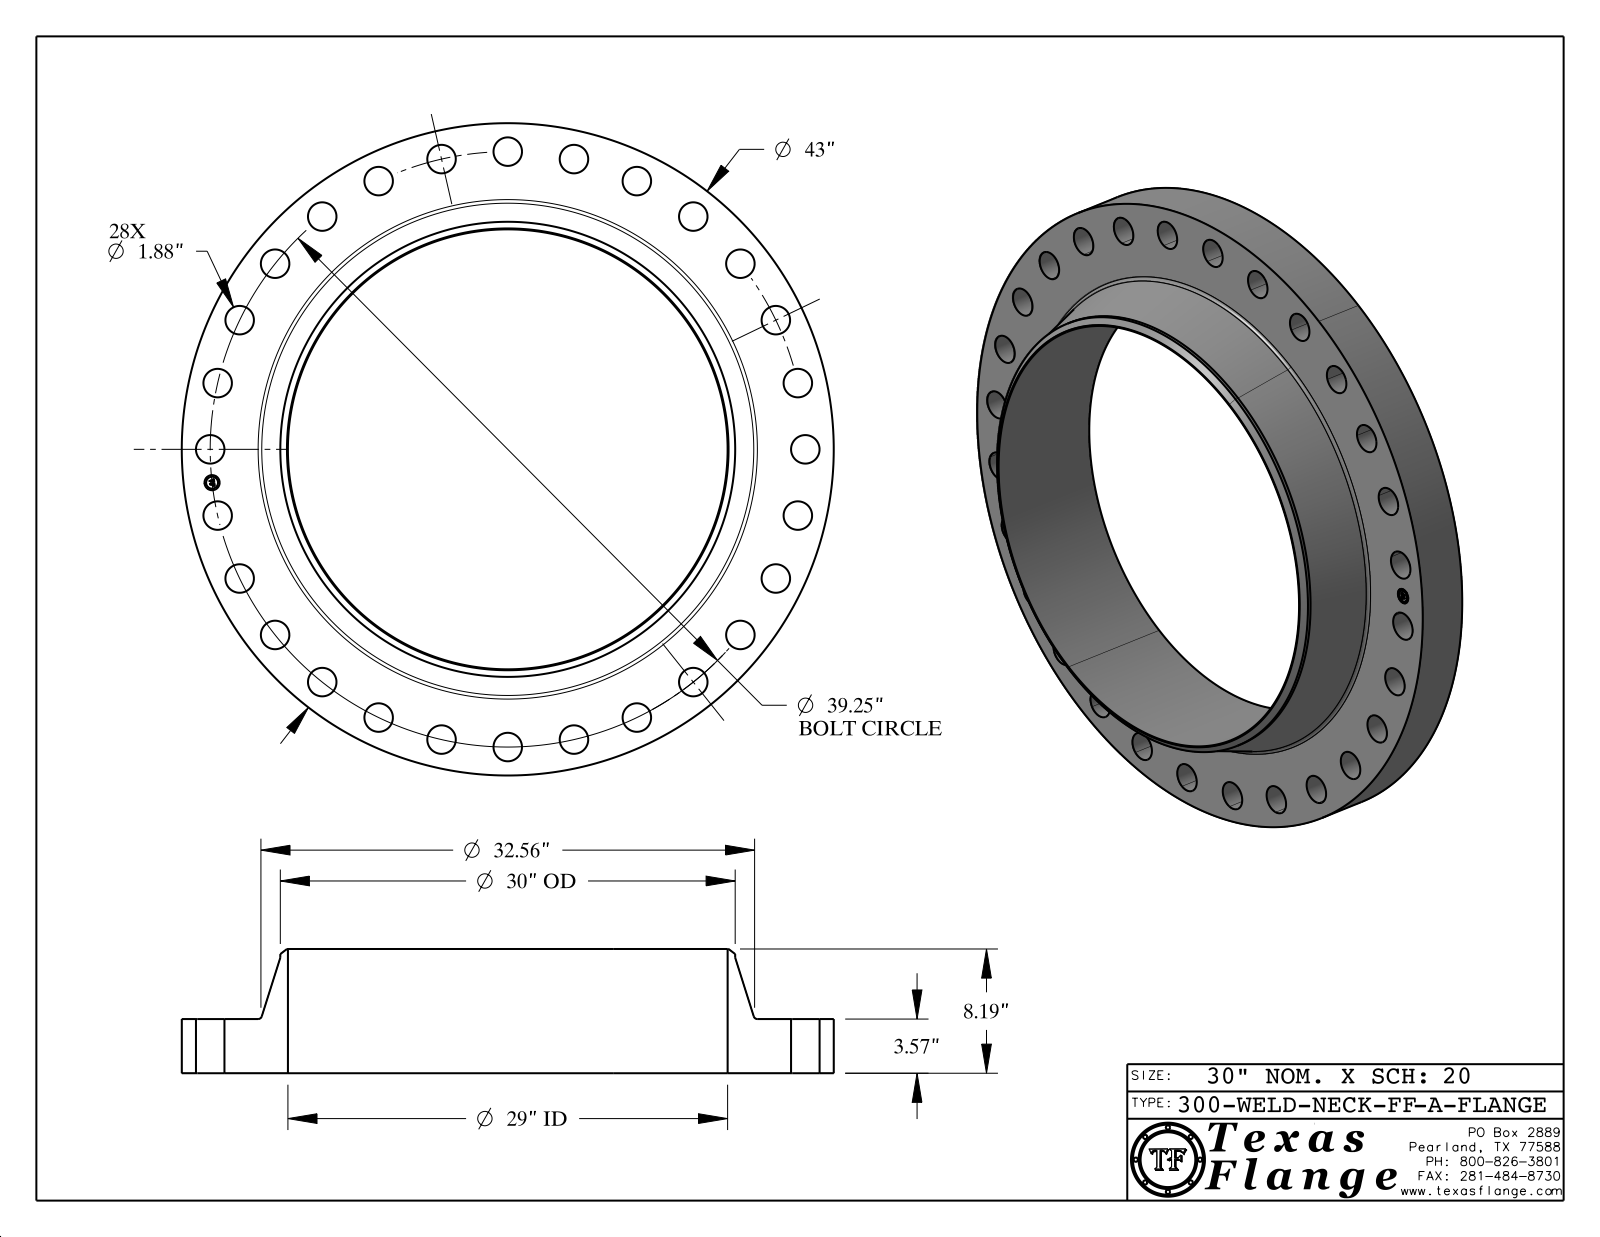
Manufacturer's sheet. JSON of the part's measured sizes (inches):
{"part_name": "300-WELD-NECK-FF, Series A", "step_written_by": "CATIA V5 STEP AP214 (AUTOMOTIVE_DESIGN)", "units": "inches", "bodies": {"solids": 1, "faces": 456, "planar": 368, "cylindrical": 82, "other": 6}, "overall_size": [43, 43, 8.19], "volume_in3": 3008, "surface_area_in2": 3566, "round_holes": [[1.88, 28], [1, 1], [29, 1]], "round_bosses_or_shafts": [[0.061, 8], [43, 1], [30, 1], [0.788, 1]], "face_to_face_distances": [3.57, 8.19, 4.62, 3.555, 0.015, 4.635, 0.298, 0.293, 0.054, 0.193], "hole_center_spacings": [4.394, 8.734, 12.963, 17.03, 20.882, 35.363, 24.472, 33.234]}
